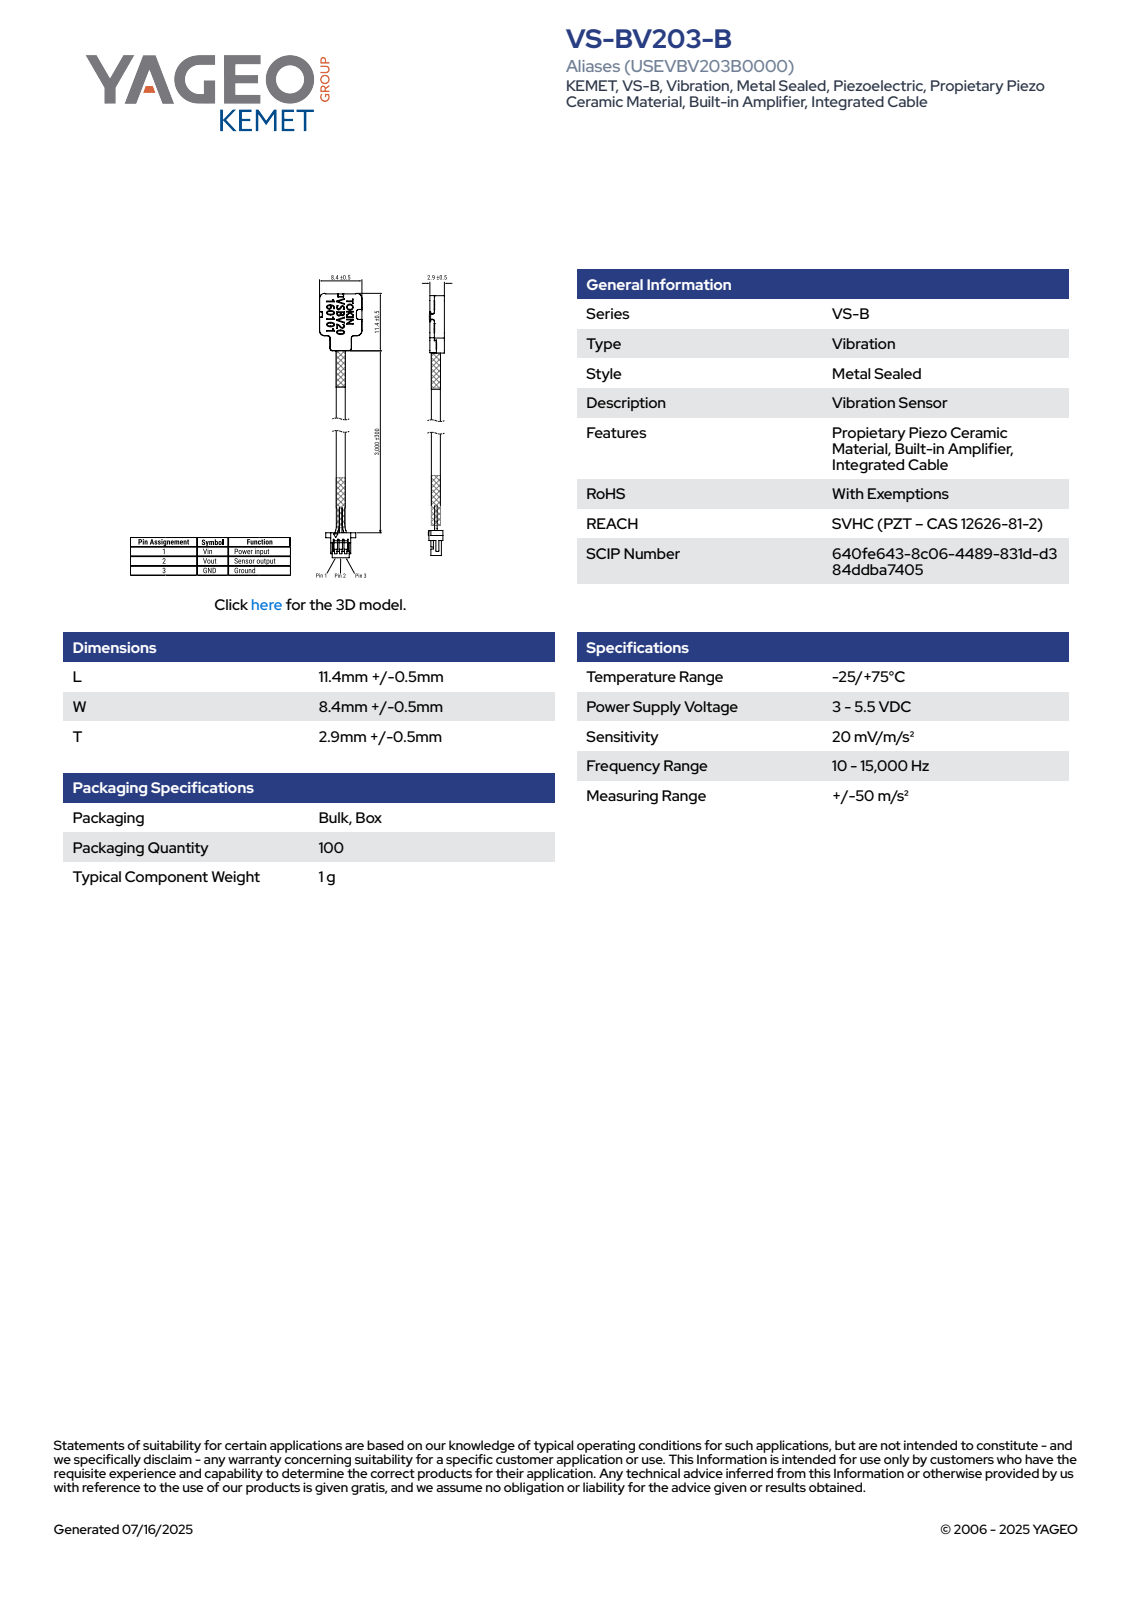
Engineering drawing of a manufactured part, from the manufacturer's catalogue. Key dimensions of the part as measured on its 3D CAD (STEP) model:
Part name (STEP PRODUCT): SV_KVSB_L11.9T3.4W8.9
STEP written by: SolidWorks 2014 (AUTOMOTIVE_DESIGN)
Units: millimetres
Bodies: 1 solid, 104 faces (64 planar, 24 cylindrical, 16 other)
Overall size (bounding box): 11.9 × 8.9 × 3.4
Volume: 311 mm³ · Surface area: 313 mm²
Partial cylindrical surfaces — rounded edges, fillets, slot ends (radius × count): R0.15 ×14, R0.25 ×4, R1 ×4
Main face-to-face distances: 3.4, 8.9, 2.05, 6.85, 11.9, 4.8, 8.65, 3.25, 3.82, 4.83
